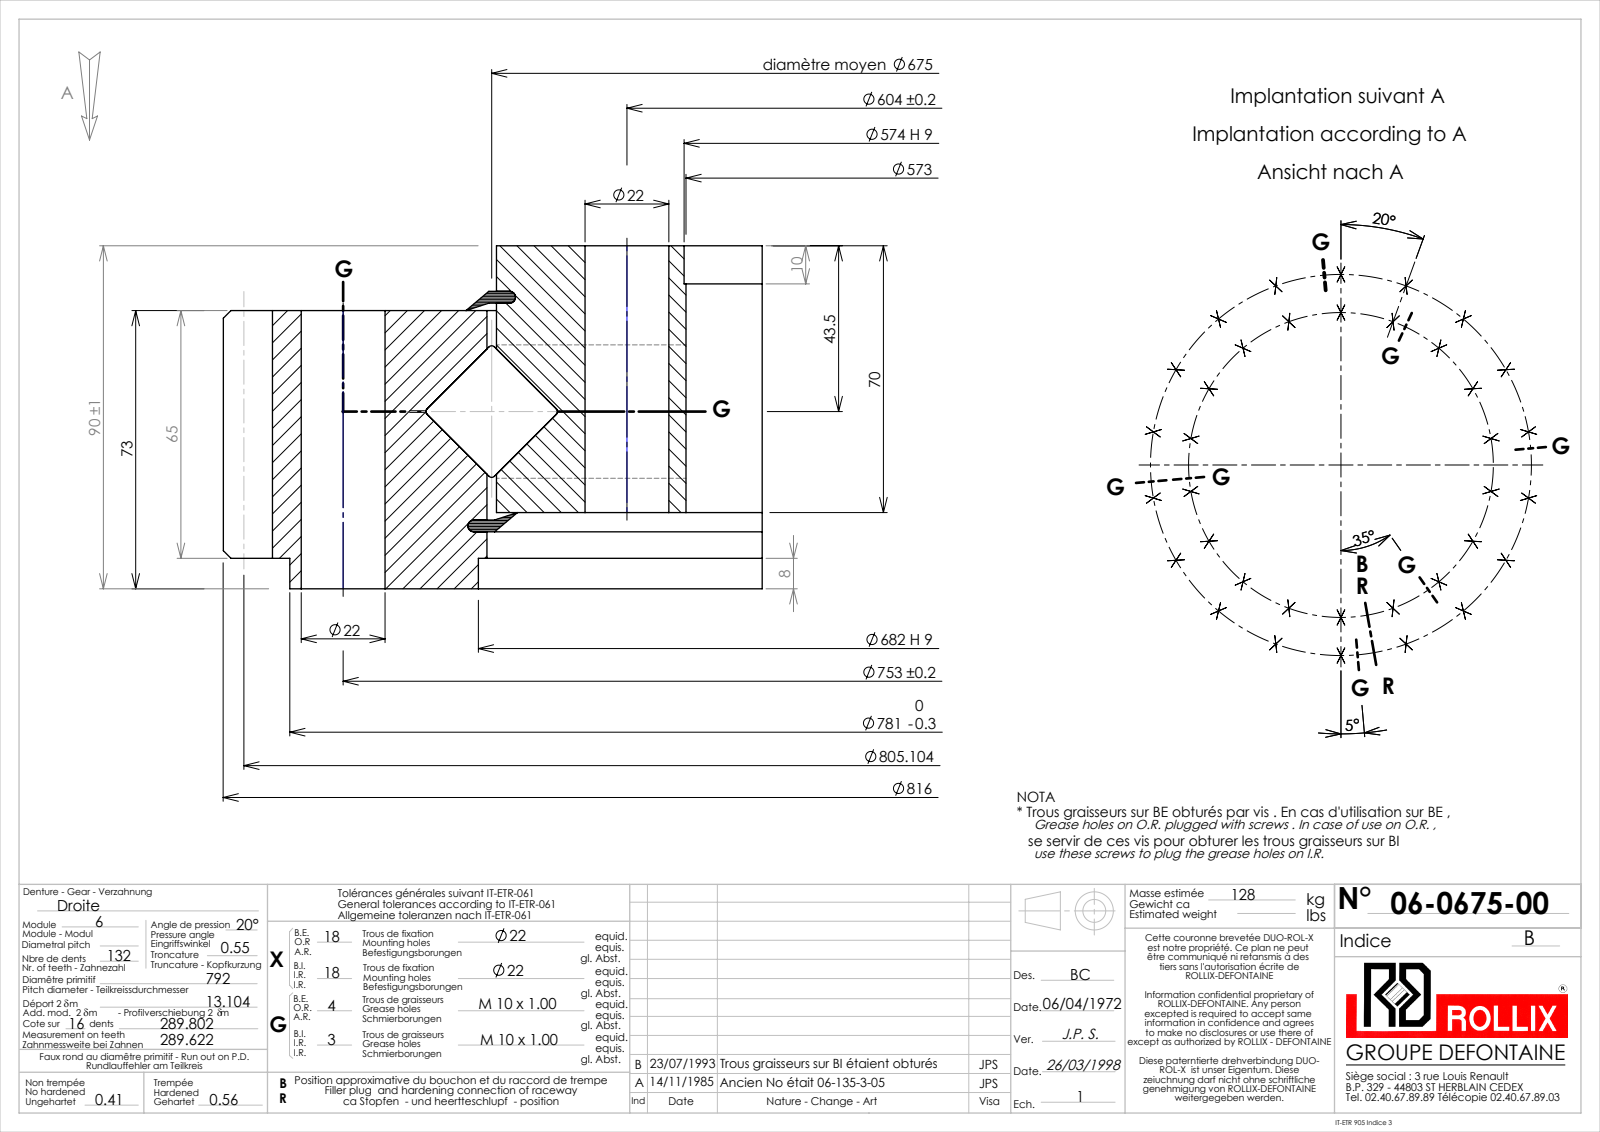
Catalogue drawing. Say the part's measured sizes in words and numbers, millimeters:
The part is named "06-0675-00". Its 3-D file was written by "SolidWorks 2016 (CONFIG_CONTROL_DESIGN)". It is 5 solids with 968 faces: 281 planar, 373 cylindrical and 314 other. Overall it measures 815.89 by 815.89 by 90 millimeters. Its volume is 15 230 000 cubic millimeters and its surface area 1 634 000 square millimeters. Round holes: 36 of diameter 22, 7 of diameter 9, 1 of diameter 573, 1 of diameter 574, 1 of diameter 677.5, 1 of diameter 682. Round bosses or shafts: 1 of diameter 781, 1 of diameter 672.5, 1 of diameter 25. Partial cylindrical surfaces (rounded edges, fillets, slot ends): 1 of radius 395.05, 1 of radius 408. The main face-to-face distances are 73, 20, 53, 90, 70, 17, 1.95, 5.05, 60, 54.95. The hole center spacings are 376.5, 257.54, 484.02, 741.56, 576.83, 707.59, 130.76, 638.09.
